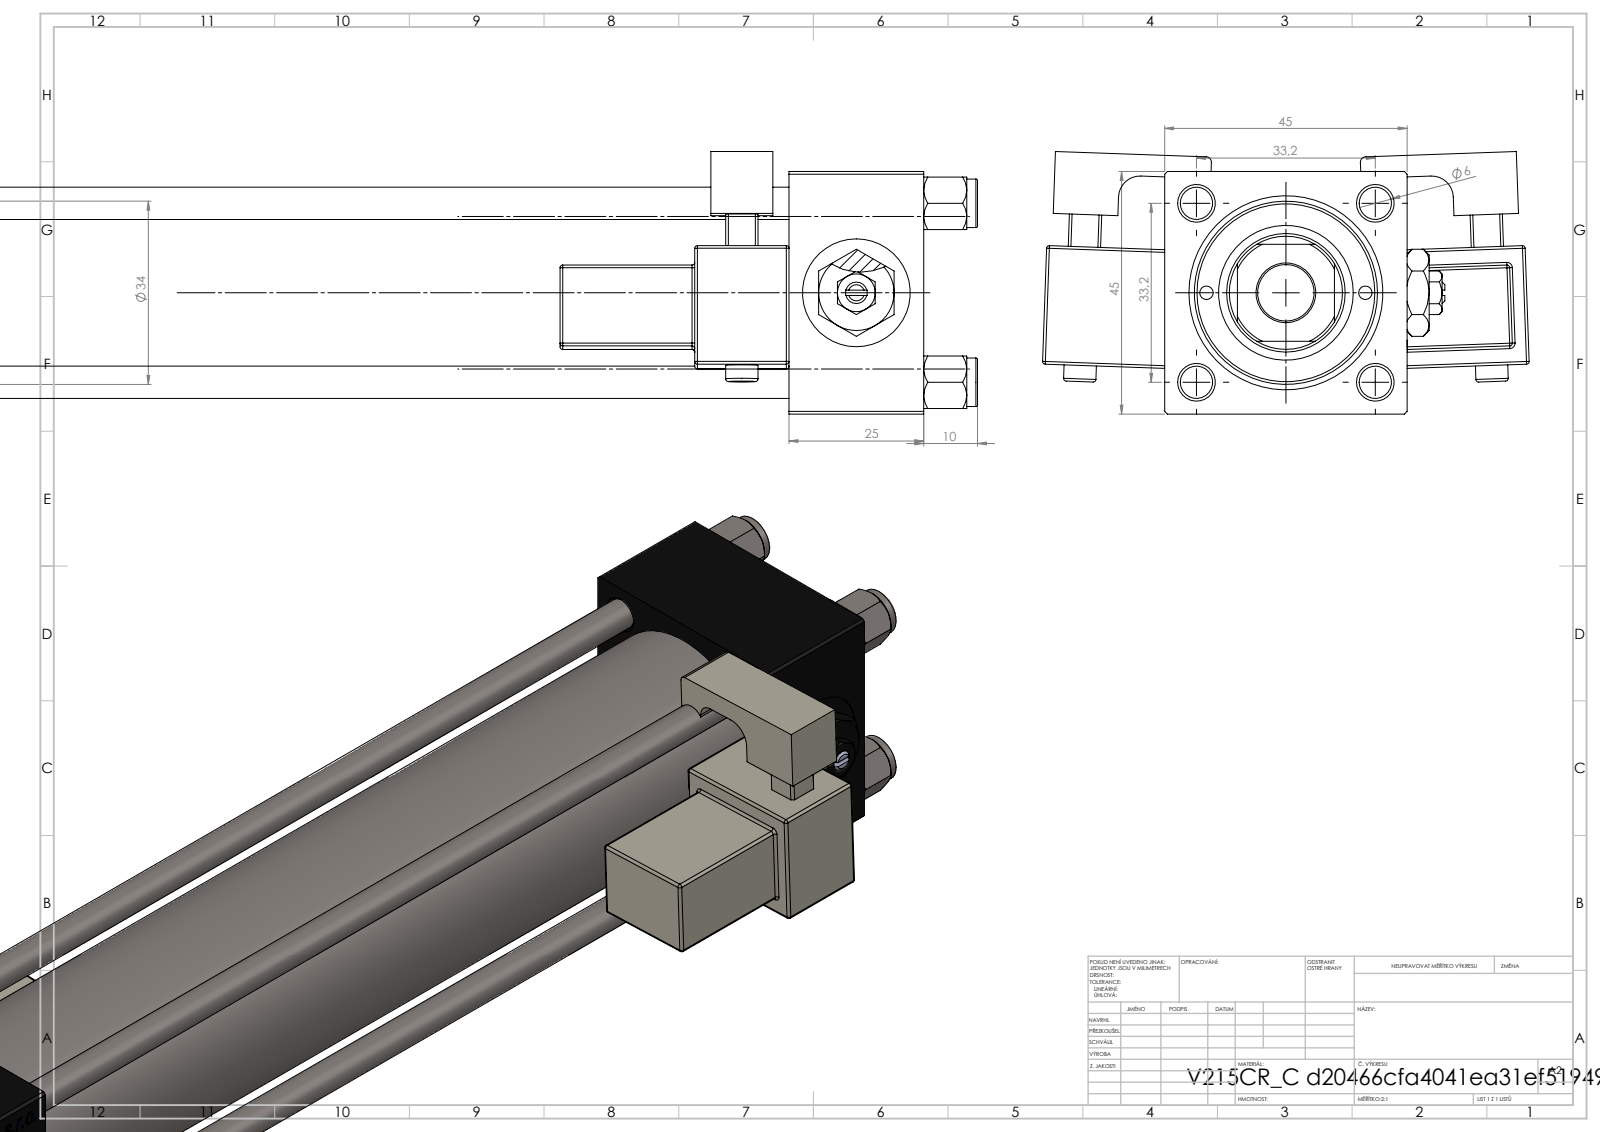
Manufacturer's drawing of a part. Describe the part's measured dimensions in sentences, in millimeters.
The part is named "V215_VC_A; NUT_M5_C; V215CR_MSU; V215CR_C_TYCINKA (+5 more)". Its 3-D file was written by "SolidWorks 2019 (CONFIG_CONTROL_DESIGN)". It is 17 solids with 1497 faces: 664 planar, 175 cylindrical and 658 other. Overall it measures 359 by 90.31 by 48.72 millimeters. Its volume is 381 910 cubic millimeters and its surface area 143 551 square millimeters. Round holes: 4 of diameter 6, 2 of diameter 2.5, 2 of diameter 7, 2 of diameter 13.16, 2 of diameter 20, 1 of diameter 10.5, 1 of diameter 22, 1 of diameter 24, 1 of diameter 25, 1 of diameter 32, 1 of diameter 33. Round bosses or shafts: 4 of diameter 9, 2 of diameter 6, 1 of diameter 38, 1 of diameter 34, 1 of diameter 28, 1 of diameter 18, 1 of diameter 12, 1 of diameter 11. Partial cylindrical surfaces (rounded edges, fillets, slot ends): 48 of radius 0.5, 2 of radius 1, 2 of radius 2.5, 2 of radius 4, 1 of radius 9.75, 1 of radius 10.5. The main face-to-face distances are 45, 25, 3, 215, 190, 263, 22.99, 44.8, 14.5, 13. The hole center spacings are 16.7, 23.48, 33.2, 35.47, 14.75, 46.95, 29.5, 215.5.
